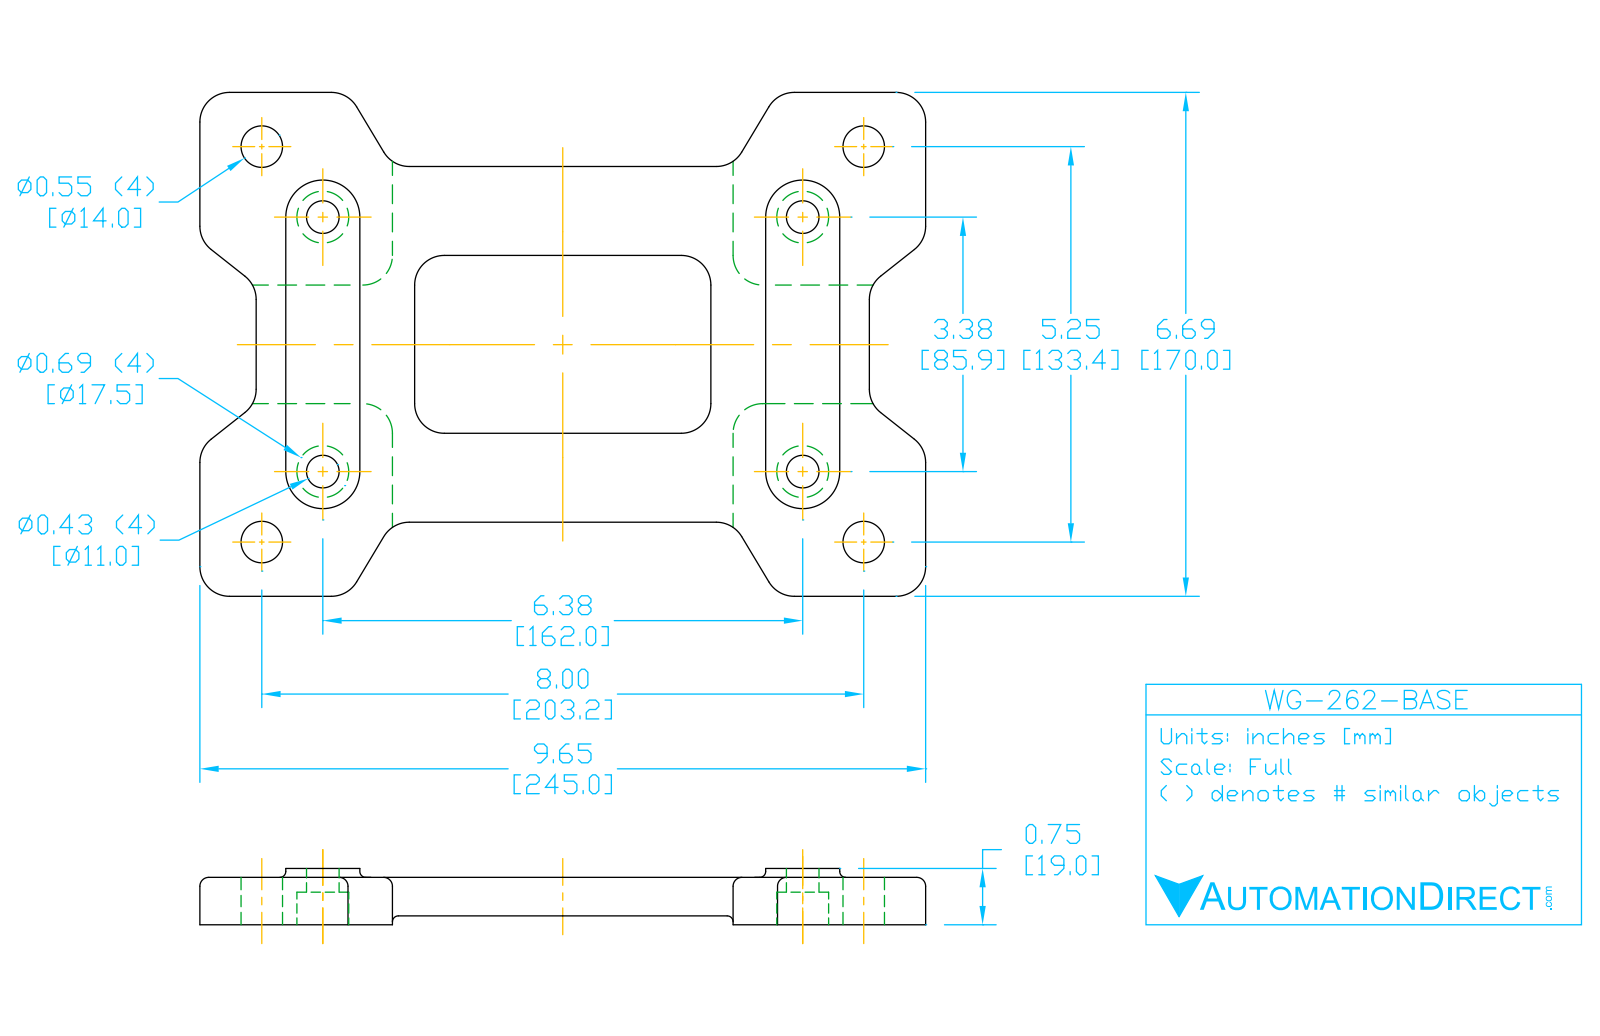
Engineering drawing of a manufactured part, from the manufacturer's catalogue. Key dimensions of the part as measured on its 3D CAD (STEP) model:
Part name (STEP PRODUCT): WG-262-BASE
STEP written by: SolidWorks 2017 (AUTOMOTIVE_DESIGN)
Units: inches
Bodies: 1 solid, 128 faces (48 planar, 70 cylindrical, 10 other)
Overall size (bounding box): 9.646 × 6.693 × 0.748
Volume: 23.94 in³ · Surface area: 120.9 in²
Round holes (diameter × count): ⌀0.433 ×4, ⌀0.551 ×4, ⌀0.689 ×4
Partial cylindrical surfaces — rounded edges, fillets, slot ends (radius × count): R0.394 ×24, R0.039 ×4, R0.079 ×4, R0.315 ×4, R0.492 ×4
Main face-to-face distances: 0.63, 0.118, 0.512, 0.748, 0.984, 5.709, 4.528, 2.165, 1.181, 3.543
Hole centre spacings: 1.238, 4.393, 7.25, 8.385, 3.382, 5.252, 6.378, 7.219
